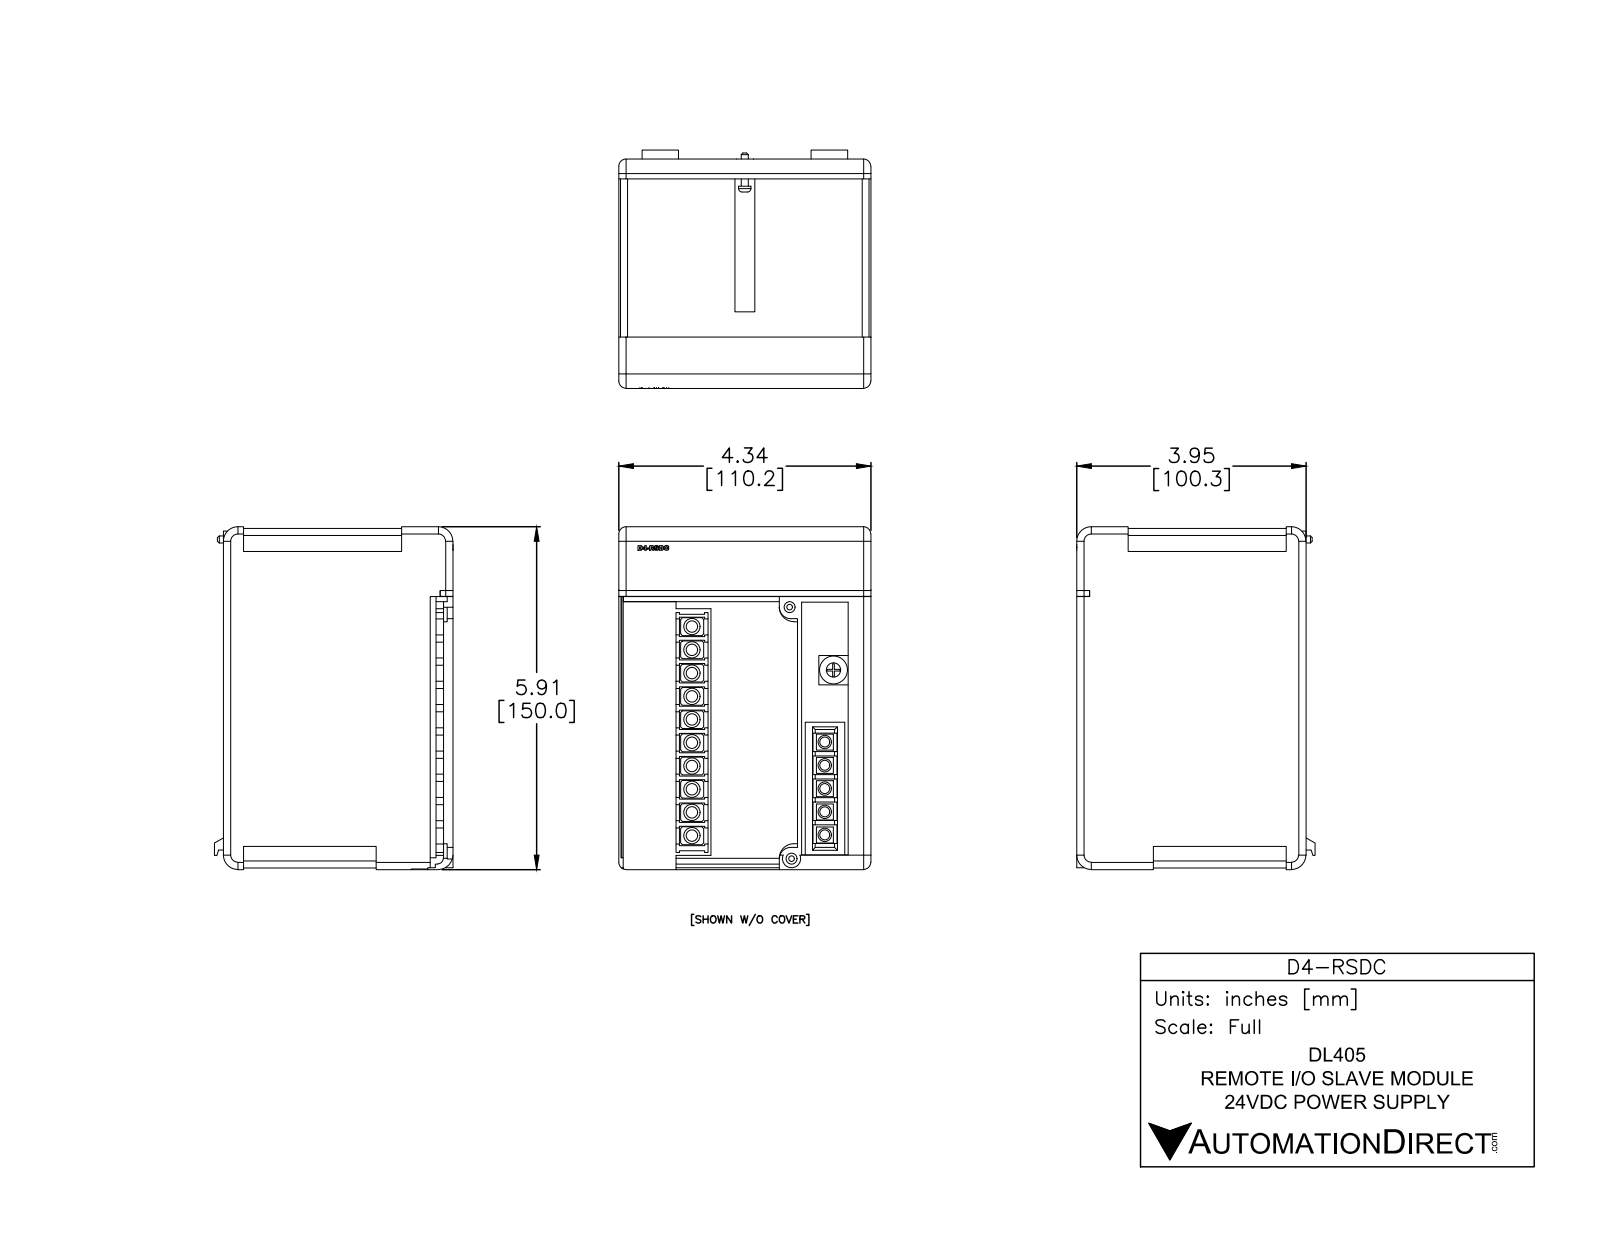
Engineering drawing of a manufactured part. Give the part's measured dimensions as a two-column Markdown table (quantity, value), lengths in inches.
| quantity | value |
| --- | --- |
| part name | D4-RSDC |
| STEP written by | SolidWorks 2014 (AUTOMOTIVE_DESIGN) |
| units | inches |
| bodies | 2 solids, 699 faces (529 planar, 83 cylindrical, 87 other) |
| overall size | 5.905 × 4.34 × 4.106 |
| volume | 93.33 in³ |
| surface area | 159.3 in² |
| round holes (diameter × count) | 0.1 × 2, 0.188 × 1, 0.188 × 1, 0.248 × 1 |
| round bosses / shafts (diameter × count) | 0.279 × 10, 0.232 × 5, 0.482 × 1, 0.212 × 1, 0.123 × 1 |
| partial cylindrical surfaces (radius × count) | 0.125 × 8, 0.25 × 6, 0.12 × 4, 0.2 × 2, 0.1 × 1, 0.145 × 1, 0.156 × 1, 0.171 × 1 |
| main face-to-face distances | 4.34, 0.03, 5.845, 5.875, 3.79, 3.95, 0.16, 0.715, 3.235, 0.555 |
| hole center spacings | 1.319, 3.325, 4.329 |
